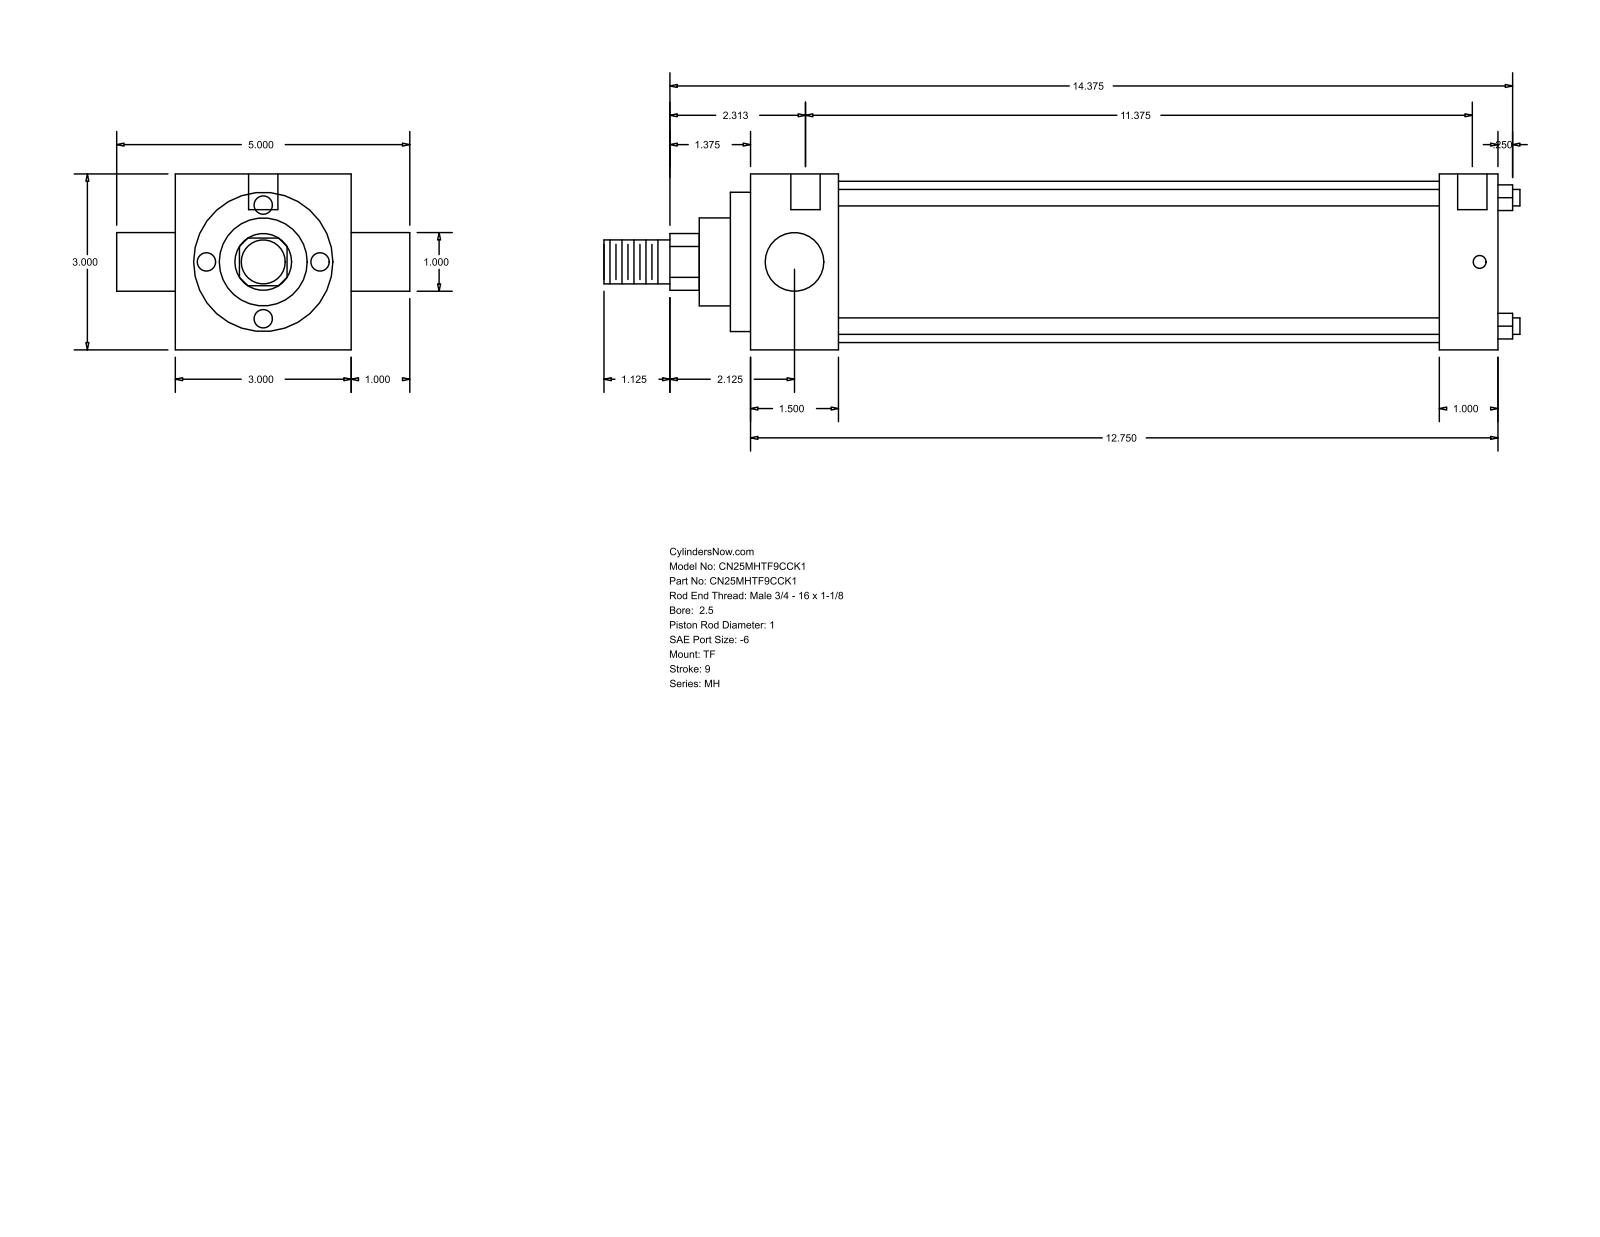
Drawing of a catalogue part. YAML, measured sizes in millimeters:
part_name: "MH_TF__0250_1"
step_written_by: "GSSL Pune (CONFIG_CONTROL_DESIGN)"
units: millimeters
bodies: {solids: 0, faces: 86, planar: 61, cylindrical: 25, other: 0}
overall_size: [396.88, 127, 76.2]
round_holes:
  - {diameter: 5.56, count: 3}
  - {diameter: 12.7, count: 2}
round_bosses_or_shafts:
  - {diameter: 7.14, count: 4}
  - {diameter: 25.4, count: 2}
  - {diameter: 69.85, count: 1}
  - {diameter: 60.33, count: 1}
  - {diameter: 38.1, count: 1}
  - {diameter: 19.05, count: 1}
partial_cylinders:
  - {radius: 12.29, count: 1}
face_to_face_distances: [76.2, 323.85, 25.39, 38.11, 285.74, 298.46, 260.35, 8.73, 46.84, 307.19]
hole_center_spacings: [3.18, 4.76, 288.92, 292.1, 293.68, 296.86]
